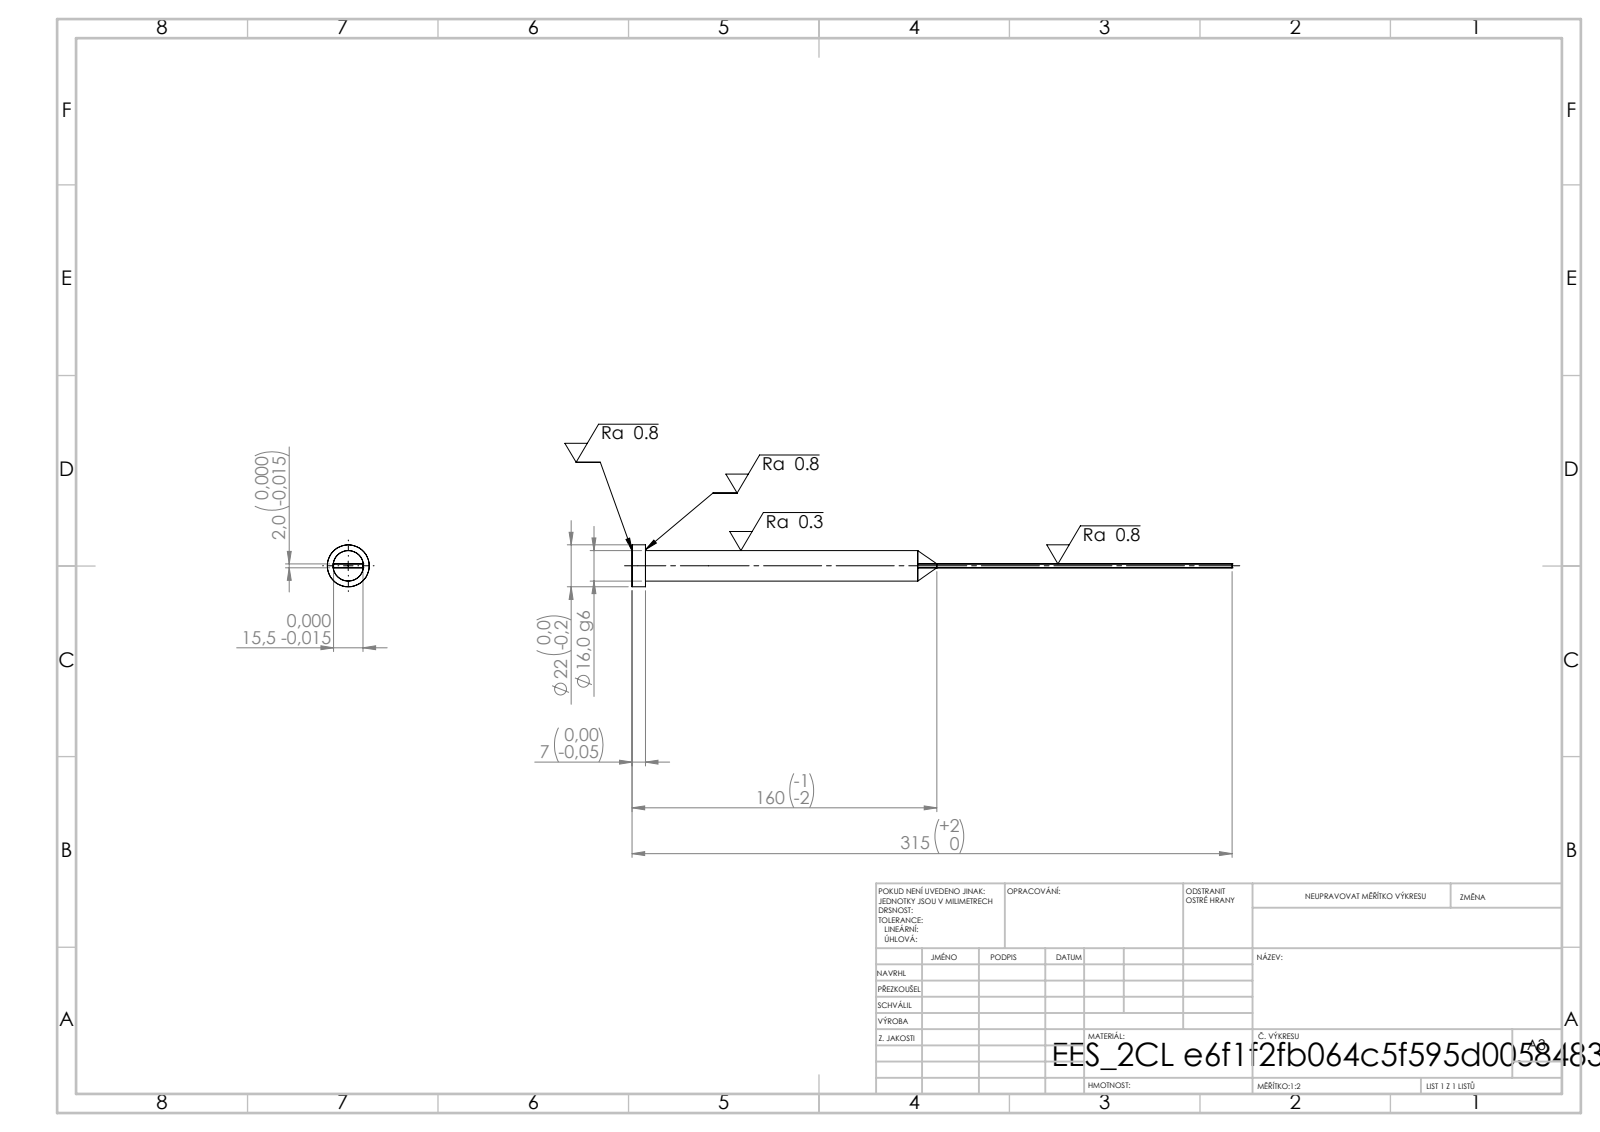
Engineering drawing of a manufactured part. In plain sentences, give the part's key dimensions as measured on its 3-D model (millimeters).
Its 3-D file was written by "SolidWorks 2019 (CONFIG_CONTROL_DESIGN)". It is 1 solid with 15 faces: 7 planar, 4 cylindrical and 4 other. Overall it measures 315 by 22 by 22 millimeters. Its volume is 37 309 cubic millimeters and its surface area 14 134 square millimeters. Round bosses or shafts: 1 of diameter 22, 1 of diameter 16. The main face-to-face distances are 2, 15.5, 7, 315, 308.
